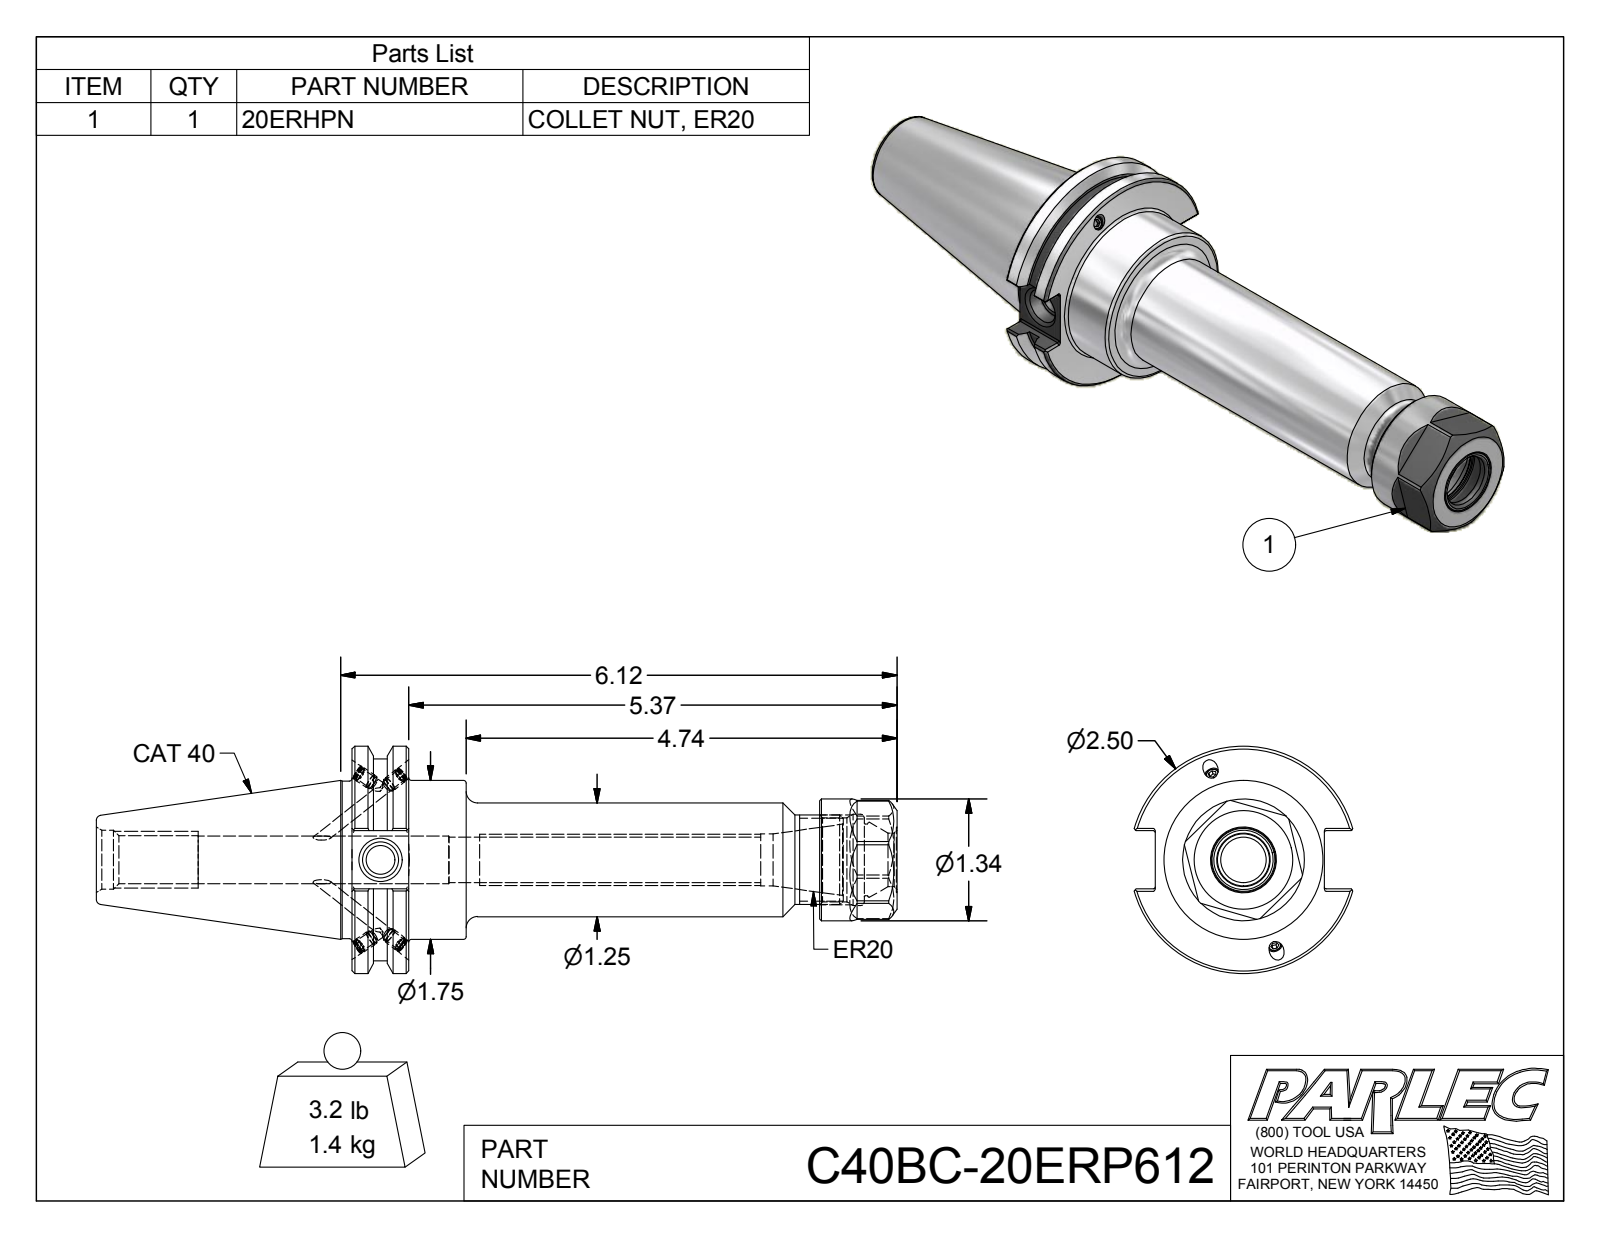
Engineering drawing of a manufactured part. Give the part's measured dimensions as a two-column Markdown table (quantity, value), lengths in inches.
| quantity | value |
| --- | --- |
| part name | C40BC-20ERP612; C40BC-20ER6-1; 029-965; 20ERHPN |
| STEP written by | Autodesk Inventor 2012 (AUTOMOTIVE_DESIGN) |
| units | inches |
| bodies | 6 solids, 200 faces (93 planar, 54 cylindrical, 53 other) |
| overall size | 8.808 × 2.5 × 2.403 |
| volume | 11.95 in³ |
| surface area | 67.16 in² |
| round holes (diameter × count) | 0.13 × 4, 0.161 × 4, 0.315 × 1, 0.399 × 1, 0.502 × 1, 0.526 × 1, 0.527 × 1, 0.57 × 1, 0.587 × 1, 0.648 × 1, 0.79 × 1, 0.926 × 1 |
| round bosses / shafts (diameter × count) | 0.165 × 4, 0.157 × 4, 2.5 × 1, 2.219 × 1, 1.75 × 1, 1.73 × 1, 1.34 × 1, 1.25 × 1 |
| partial cylindrical surfaces (radius × count) | 0.02 × 12 |
| main face-to-face distances | 0.625, 5.145, 4.52, 5.995, 5.37, 0.85, 1.18, 1.255, 0.63, 3.89 |
